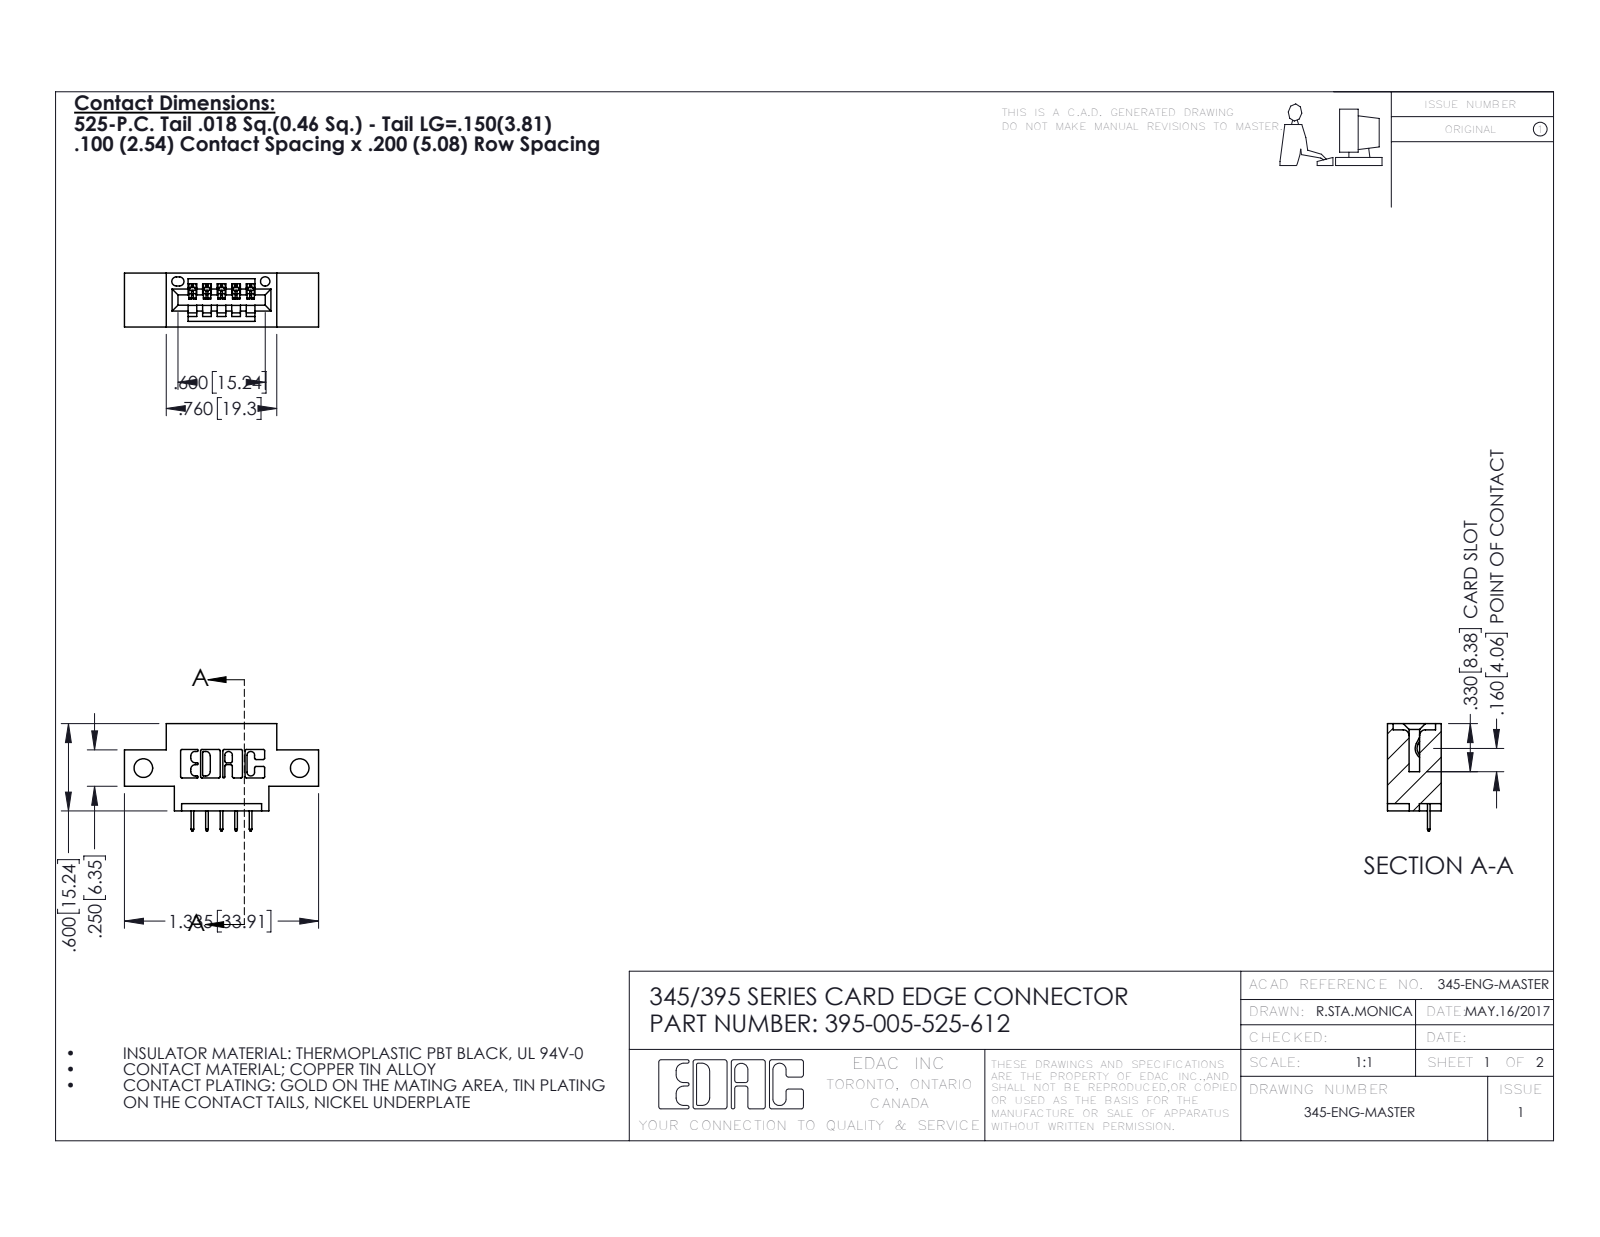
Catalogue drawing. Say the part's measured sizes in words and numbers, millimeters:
The part is named "345 Part_0.170 Offset - Side Mount; 395-005-525-612; 345-292-001_345-293-125". Its 3-D file was written by "SolidWorks 2020 (CONFIG_CONTROL_DESIGN)". It is 6 solids with 440 faces: 314 planar, 126 cylindrical and 0 other. Overall it measures 33.9 by 18.7 by 9.4 millimeters. Its volume is 2 700 cubic millimeters and its surface area 2 997 square millimeters. Round holes: 2 of diameter 3.3, 1 of diameter 1.6. Partial cylindrical surfaces (rounded edges, fillets, slot ends): 22 of radius 0.3, 10 of radius 0.2, 6 of radius 0.2, 6 of radius 0.8, 3 of radius 0.7, 2 of radius 0.8, 2 of radius 1, 1 of radius 0.4. The main face-to-face distances are 9.4, 5.1, 2.5, 1.8, 7.6, 6.4, 0.6, 1.5, 14, 3.8. The hole center spacings are 27.3.
